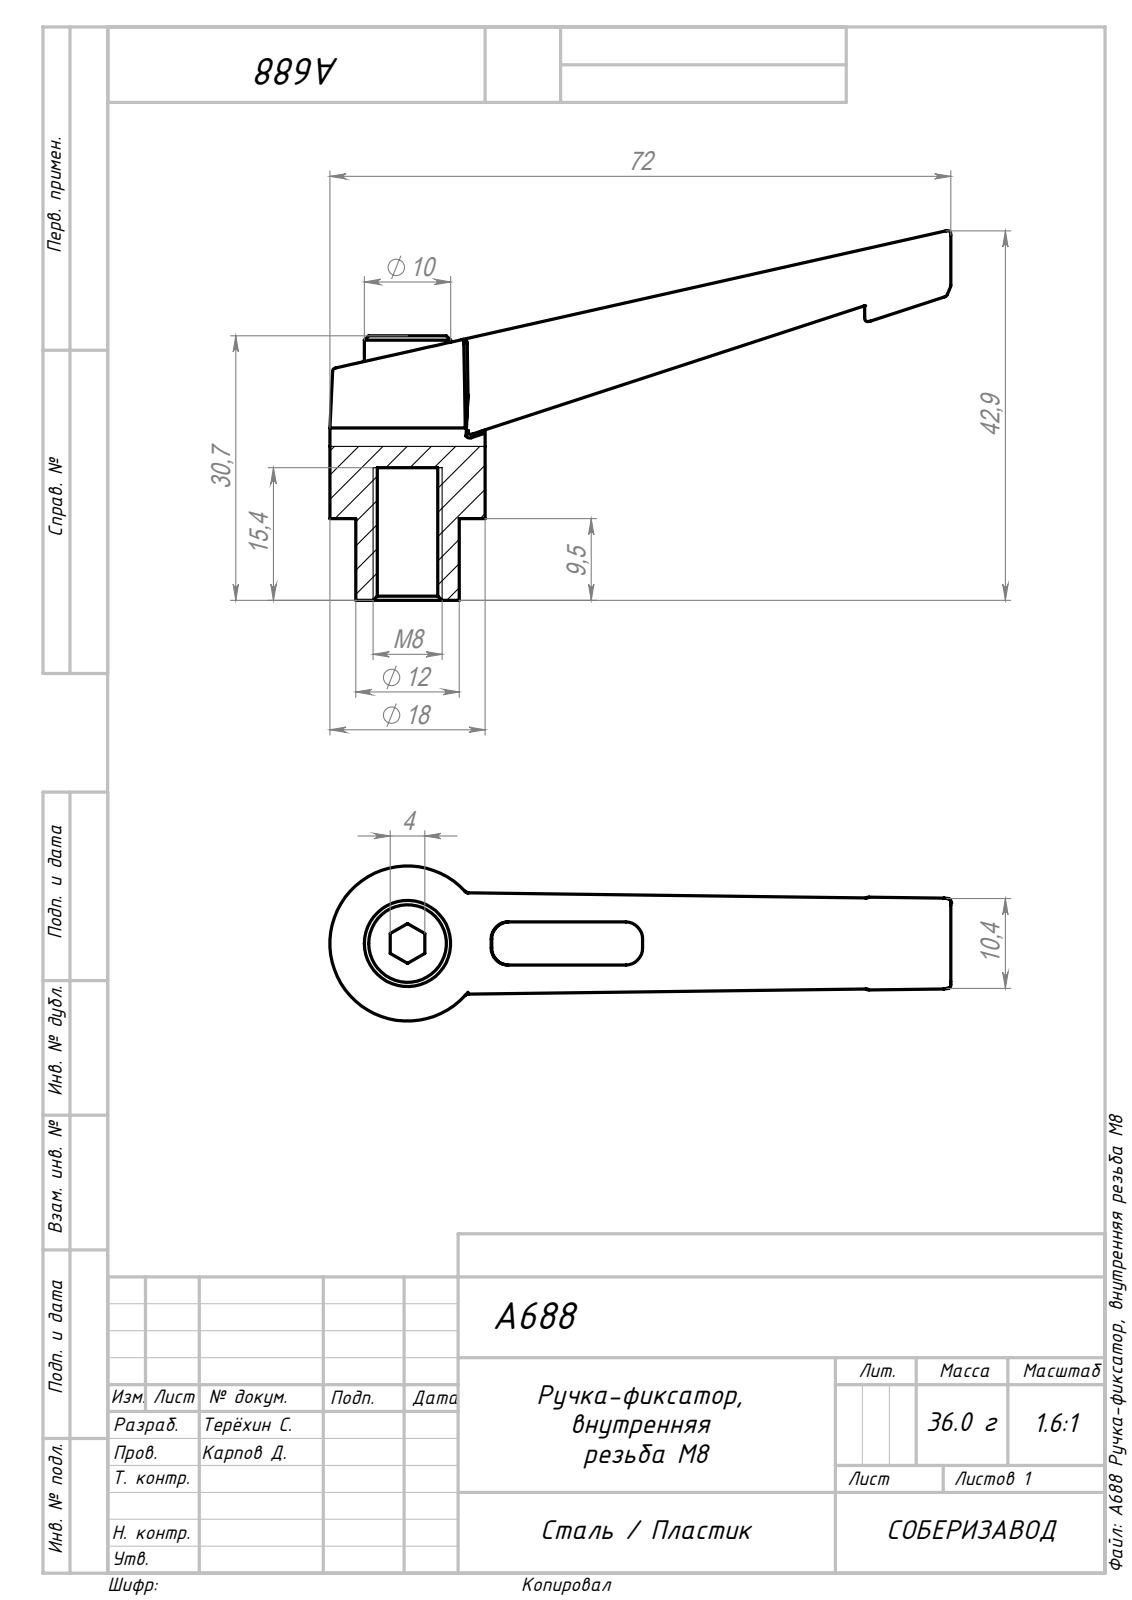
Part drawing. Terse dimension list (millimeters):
name: A688 Ручка-фиксатор, внутренняя резьба М8
written by: SolidWorks 2022 (AUTOMOTIVE_DESIGN)
unit: mm
bodies: 1 solid, 85 faces (31 planar, 12 cylindrical, 42 other)
size: 72 × 42.9 × 18
volume: 8 102 mm³; area: 5 041 mm²
holes: 1× ⌀7
bosses: 1× ⌀18, 1× ⌀12, 1× ⌀10
rounds: 4× R2
face distances: 6.9, 0.33, 9.5, 30.7, 21.2, 46.58, 15.4, 5.9, 15.3, 4
